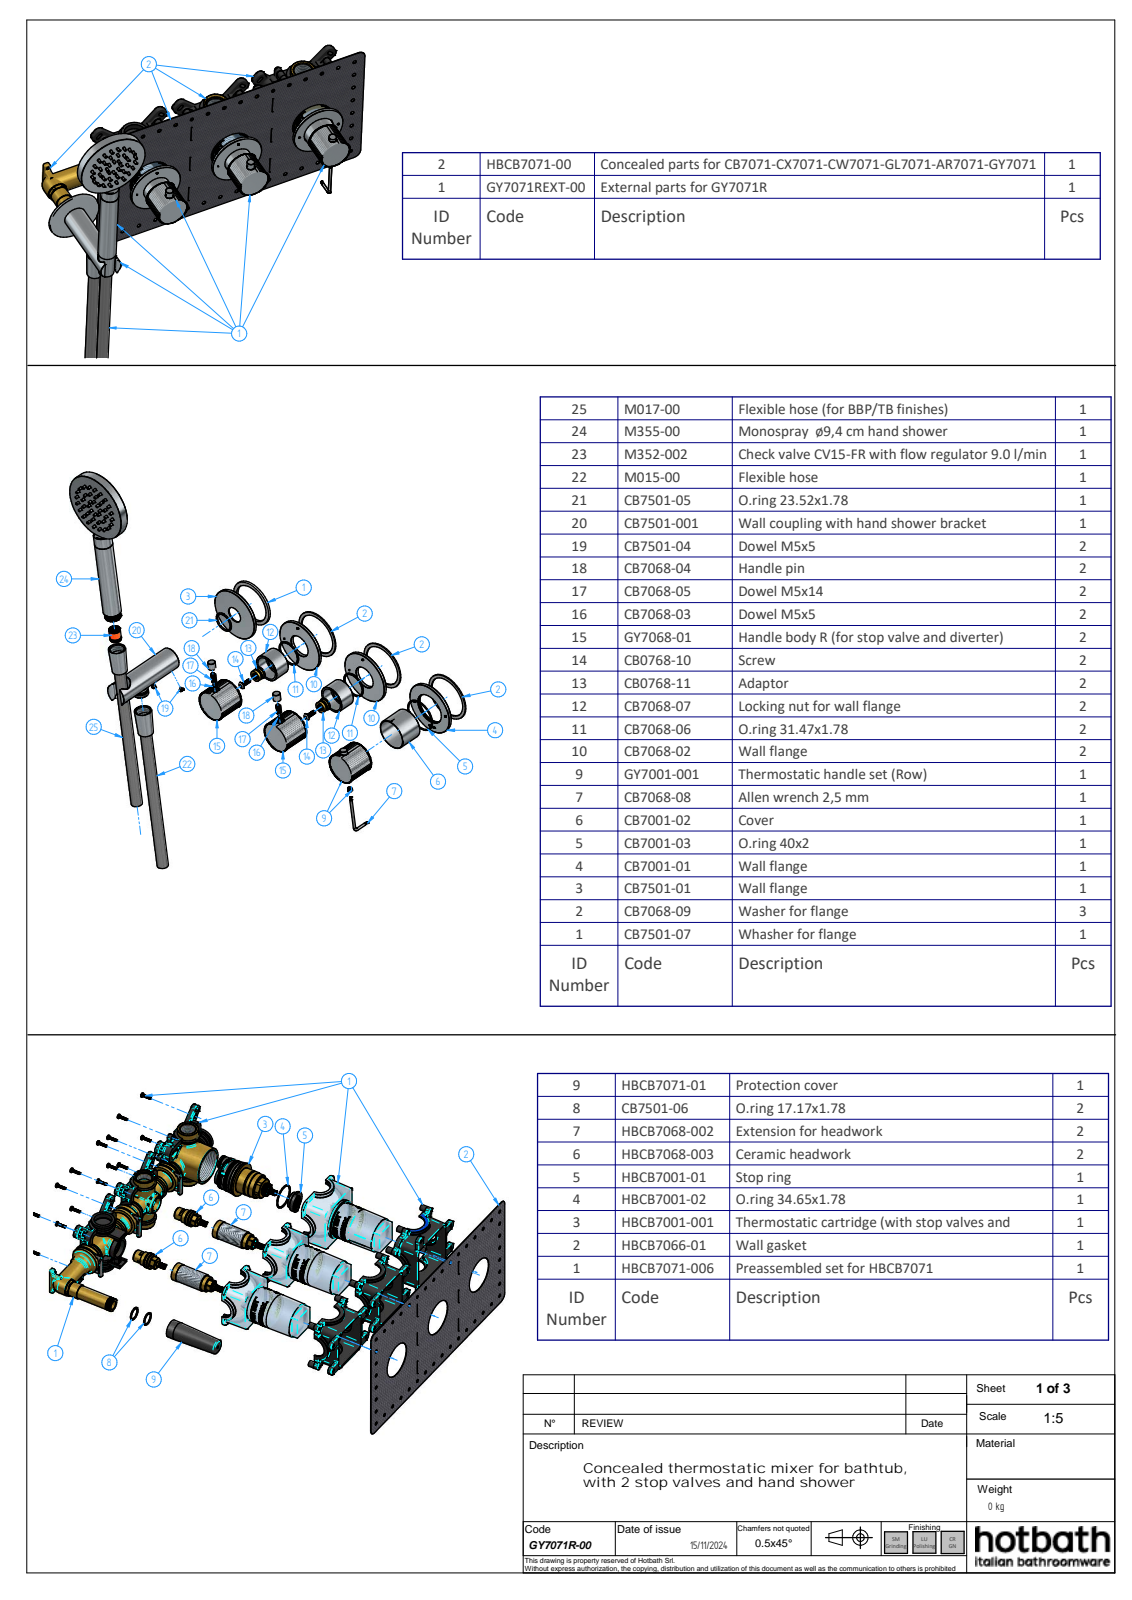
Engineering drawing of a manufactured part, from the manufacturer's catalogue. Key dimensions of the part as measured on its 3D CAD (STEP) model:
Part name (STEP PRODUCT): GY7071REXT-00; CB7501-05; CB7501-04; CB7501-01 (+8 more)
STEP written by: Solid Edge (AUTOMOTIVE_DESIGN)
Units: millimetres
Bodies: 47 solids, 4021 faces (1126 planar, 1197 cylindrical, 1698 other)
Overall size (bounding box): 501.74 × 361.48 × 355.93
Volume: 405 071 mm³ · Surface area: 210 954 mm²
Round holes (diameter × count): ⌀0.7 ×40, ⌀4.13 ×5, ⌀5.2 ×3, ⌀15.2 ×3, ⌀38 ×3, ⌀57 ×3, ⌀67 ×3, ⌀4 ×2, ⌀4.5 ×2, ⌀10.5 ×2, ⌀16.5 ×2, ⌀18.63 ×2
Round bosses / shafts (diameter × count): ⌀5 ×5, ⌀4 ×5, ⌀72 ×4, ⌀66 ×3, ⌀15.15 ×3, ⌀10 ×3, ⌀37 ×2, ⌀21 ×2
Partial cylindrical surfaces — rounded edges, fillets, slot ends (radius × count): R0.1 ×531, R4.5 ×12, R0.2 ×8, R0.81 ×3, R9.5 ×3, R18.5 ×3, R21 ×3, R0.56 ×2
Main face-to-face distances: 10, 2, 12, 10.1, 1.9, 4, 87.85, 3.95, 48.1, 52.1
Hole centre spacings: 63.21, 10.01, 37.62, 19.78, 45.25, 51.78, 60.87, 29.05
